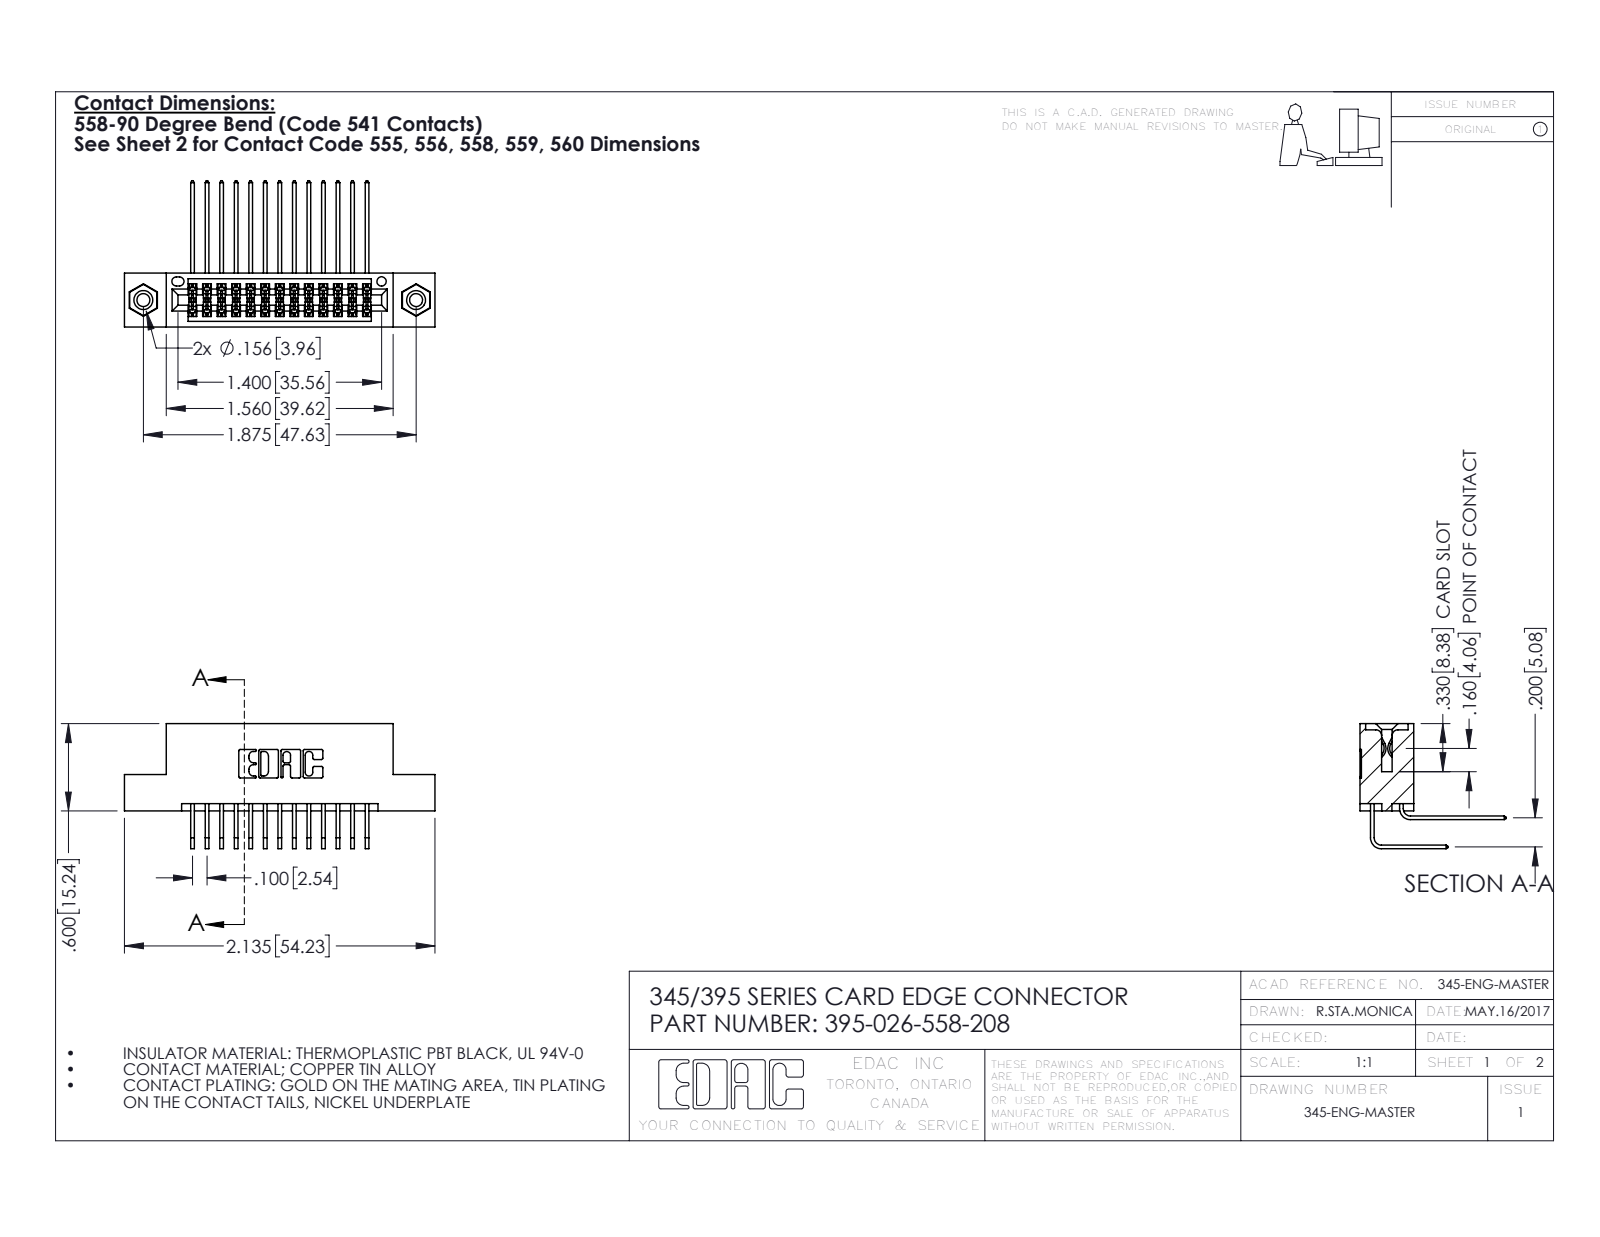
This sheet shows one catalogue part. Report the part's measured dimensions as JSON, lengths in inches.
{"part_name": "345-292-001_558 559 Tail - 1; 345-292-001_558 Tail - 2; 345 Part_Flush Mounting Lugs - 0.156 Dia-TI; 395-026-558-208 (+1 more)", "step_written_by": "SolidWorks 2016 (CONFIG_CONTROL_DESIGN)", "units": "inches", "bodies": {"solids": 29, "faces": 1538, "planar": 1022, "cylindrical": 500, "other": 16}, "overall_size": [2.135, 1.005, 0.859], "volume_in3": 0.314, "surface_area_in2": 12.02, "round_holes": [[0.089, 2], [0.125, 2], [0.156, 2], [0.064, 1]], "round_bosses_or_shafts": [[0.155, 2]], "partial_cylinders_radius": [[0.006, 40], [0.01, 22], [0.007, 6], [0.031, 6], [0.026, 3], [0.014, 2], [0.019, 2], [0.022, 2]], "face_to_face_distances": [0.2, 0.072, 0.298, 0.37, 0.098, 0.272, 0.025, 0.225, 0.1, 0.285], "hole_center_spacings": [0.27, 1.643, 1.875]}
